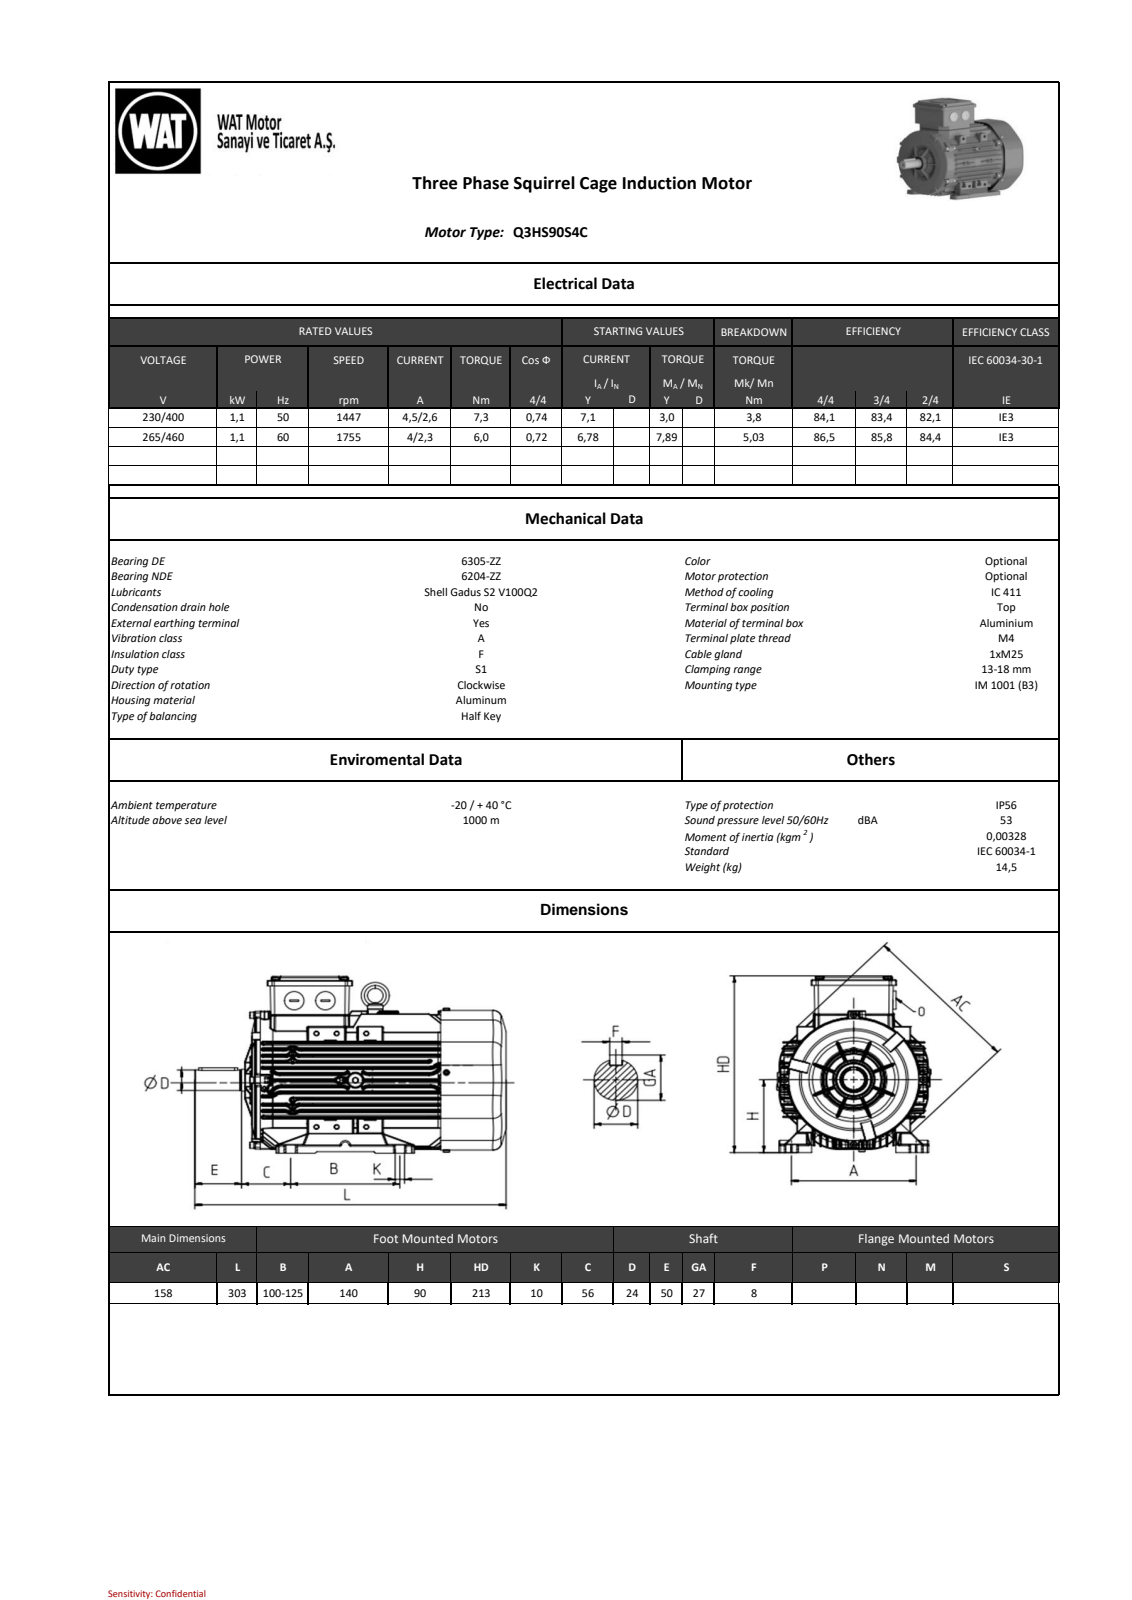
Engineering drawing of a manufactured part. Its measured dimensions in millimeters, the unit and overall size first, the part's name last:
Units: millimetres
Overall size (bounding box): 303 × 211.5 × 162.94
Round holes (diameter × count): ⌀3 ×2, ⌀4.6 ×2, ⌀3.5 ×1, ⌀8 ×1, ⌀8.4 ×1, ⌀40 ×1, ⌀57.4 ×1
Round bosses / shafts (diameter × count): ⌀6 ×8, ⌀11.6 ×4, ⌀9.3 ×4, ⌀8.33 ×4, ⌀10 ×2, ⌀146.5 ×1, ⌀143 ×1, ⌀61 ×1
Partial cylindrical surfaces — rounded edges, fillets, slot ends (radius × count): R0.5 ×855, R1 ×472, R0.8 ×324, R2 ×53, R1.5 ×16, R4 ×15, R5 ×13, R10 ×8
Main face-to-face distances: 1, 138, 18, 156, 4, 153, 157, 46.5, 199.5, 41.96
Hole centre spacings: 25.5, 25.58, 44.17, 70.87
Bodies: 0 solids, 6011 faces (1384 planar, 2502 cylindrical, 2125 other)
Part name (STEP PRODUCT): 001_objects
STEP written by: SIEMENS PLM Software NX2206.8101 (AUTOMOTIVE_DESIGN)
